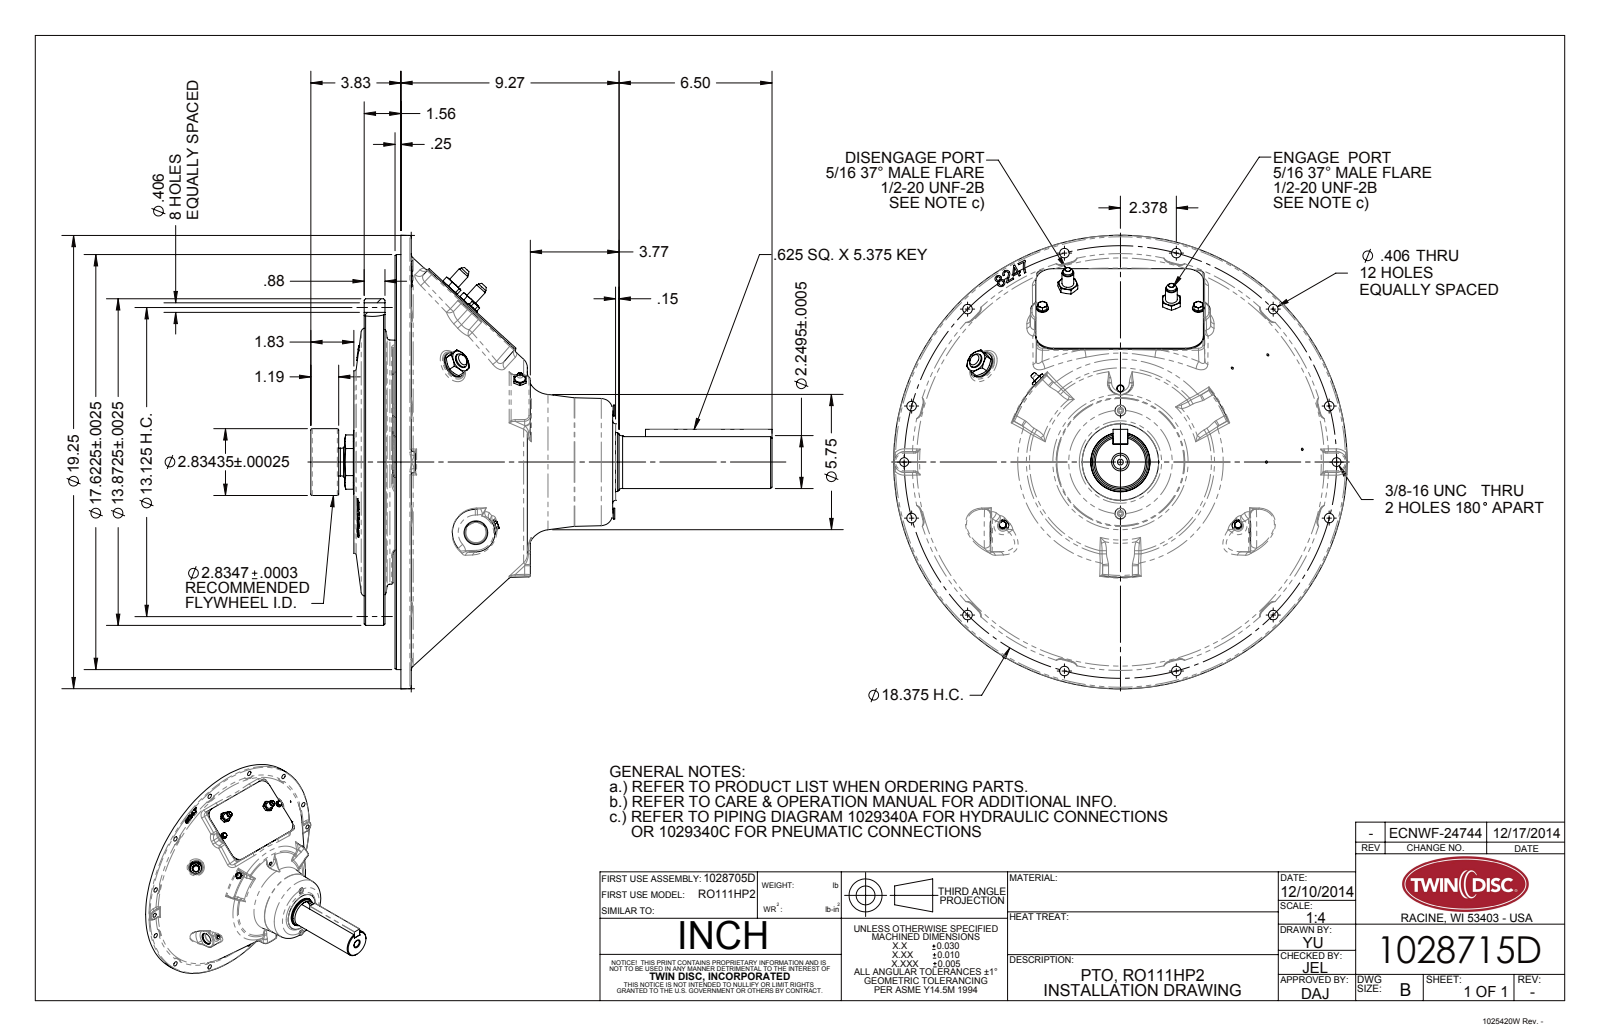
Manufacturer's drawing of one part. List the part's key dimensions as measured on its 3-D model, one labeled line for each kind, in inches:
Part name (STEP PRODUCT): 1028715D
STEP written by: SolidWorks 2010 (AUTOMOTIVE_DESIGN)
Units: inches
Bodies: 0 solids, 1008 faces (267 planar, 198 cylindrical, 543 other)
Overall size (bounding box): 19.602 × 19.273 × 19.273
Round holes (diameter × count): ⌀0.406 ×20, ⌀0.104 ×4, ⌀0.375 ×4, ⌀0.234 ×2, ⌀0.422 ×2, ⌀0.875 ×2, ⌀1.008 ×1, ⌀1.181 ×1, ⌀1.936 ×1, ⌀2.428 ×1, ⌀11.787 ×1
Round bosses / shafts (diameter × count): ⌀0.5 ×4, ⌀0.46 ×2, ⌀0.426 ×2, ⌀17.622 ×1, ⌀13.872 ×1, ⌀11.375 ×1, ⌀2.834 ×1, ⌀2.7 ×1
Partial cylindrical surfaces — rounded edges, fillets, slot ends (radius × count): R0.25 ×20, R0.03 ×12, R0.06 ×12, R0.125 ×6, R0.75 ×4, R2.052 ×4, R2.1 ×3, R0.01 ×2
Main face-to-face distances: 1.387, 0.437, 1.824, 1.997, 1.56, 0.173, 0.064, 0.439, 2.436, 1.998
Hole centre spacings: 9.187, 6.497, 11.291, 12.993, 14.586, 17.749, 3.317, 4.756
